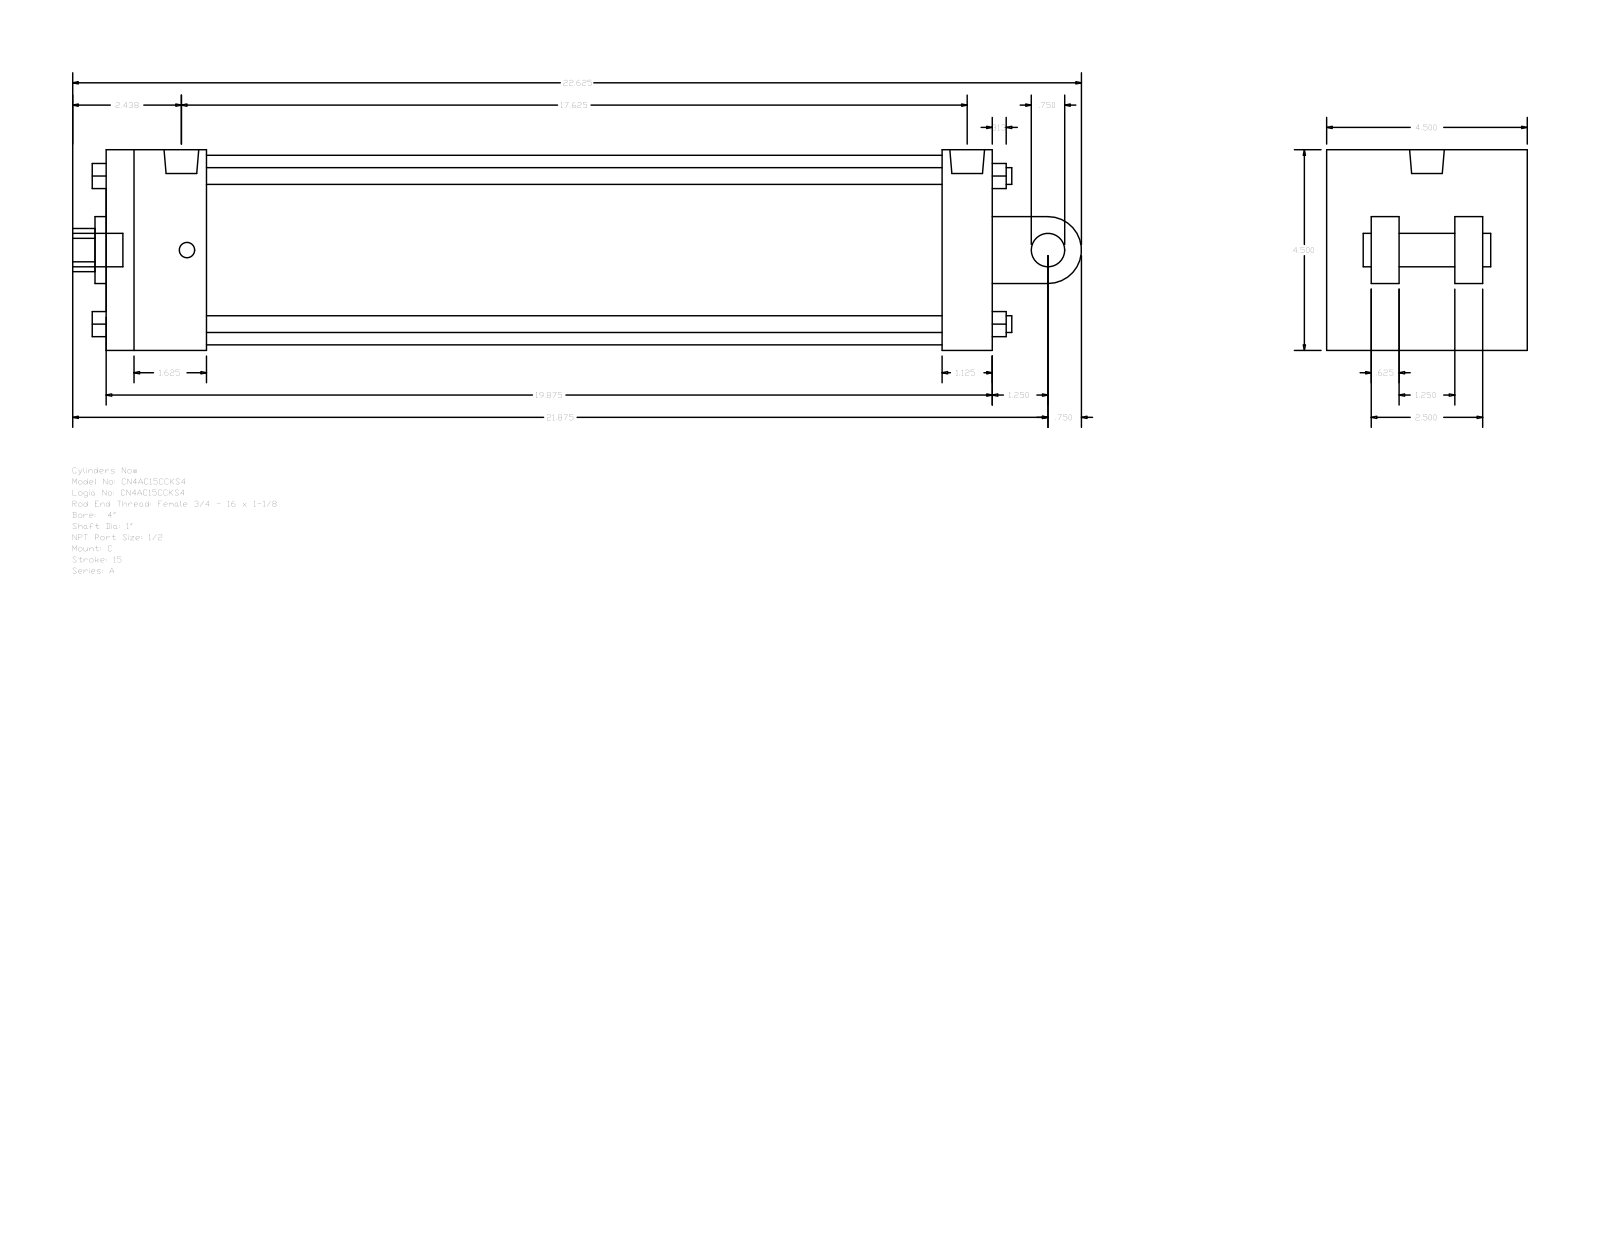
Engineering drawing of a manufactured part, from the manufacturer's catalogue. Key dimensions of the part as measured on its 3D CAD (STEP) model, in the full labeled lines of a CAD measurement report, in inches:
Part name (STEP PRODUCT): A_C__0400_1
STEP written by: GSSL Pune (CONFIG_CONTROL_DESIGN)
Units: inches
Bodies: 0 solids, 135 faces (102 planar, 33 cylindrical, 0 other)
Overall size (bounding box): 22.625 × 4.5 × 4.5
Round holes (diameter × count): ⌀0.344 ×2, ⌀0.778 ×1, ⌀1 ×1, ⌀1.5 ×1, ⌀4.25 ×1
Round bosses / shafts (diameter × count): ⌀0.375 ×4, ⌀0.75 ×2, ⌀0.344 ×2, ⌀0.778 ×1
Partial cylindrical surfaces — rounded edges, fillets, slot ends (radius × count): R0.484 ×1, R0.75 ×1
Main face-to-face distances: 4.5, 19.875, 2.875, 18.75, 1.125, 2.25, 16.5, 17.625, 0.625, 1.875
Hole centre spacings: 0.125
